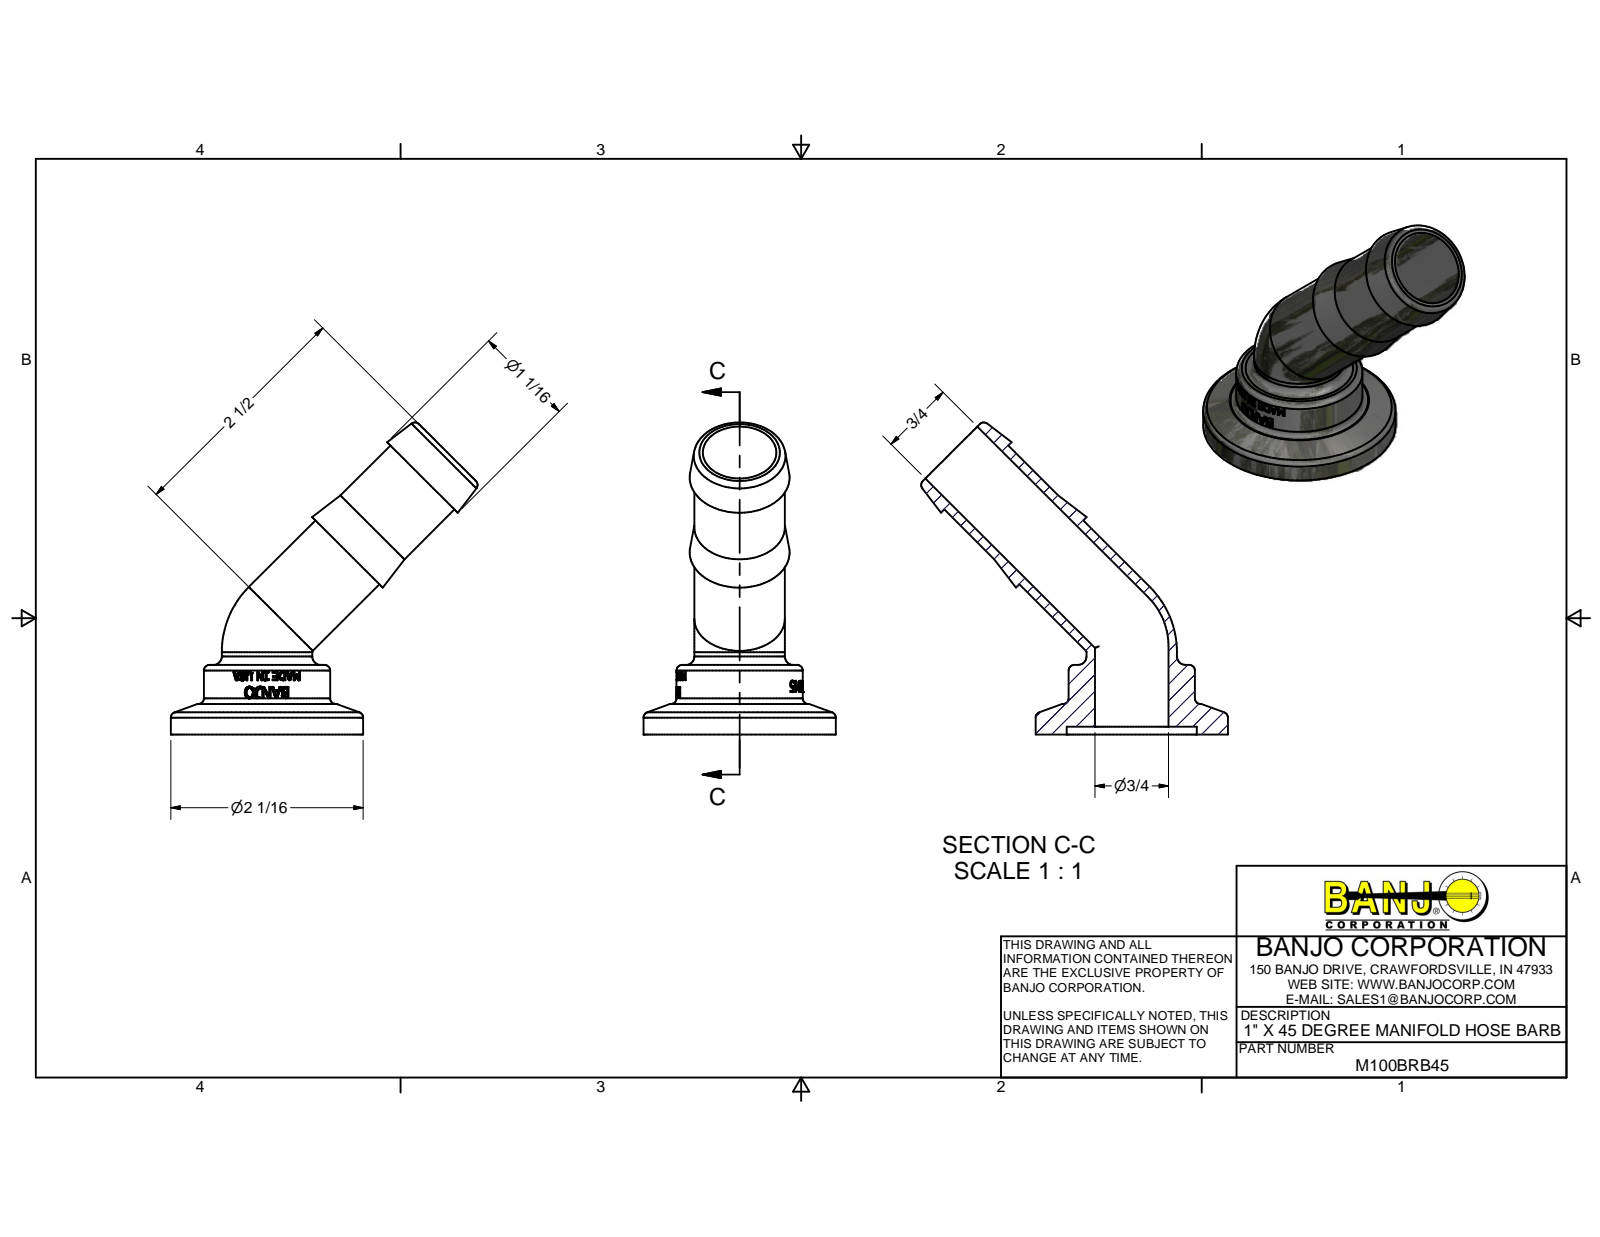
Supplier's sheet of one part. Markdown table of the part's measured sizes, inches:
| quantity | value |
| --- | --- |
| part name | M100BRB45 |
| STEP written by | Autodesk Inventor 2010 (AUTOMOTIVE_DESIGN) |
| units | inches |
| bodies | 1 solid, 422 faces (170 planar, 66 cylindrical, 186 other) |
| overall size | 3.316 × 3.254 × 2.04 |
| volume | 1.928 in³ |
| surface area | 27.99 in² |
| round bosses / shafts (diameter × count) | 0.96 × 2, 2.04 × 1, 1.34 × 1 |
| partial cylindrical surfaces (radius × count) | 0.64 × 1 |
| main face-to-face distances | 1.125, 0.74, 1.5, 0.375, 0.416, 0.324, 0.065, 0.12, 0.164, 0.252 |
